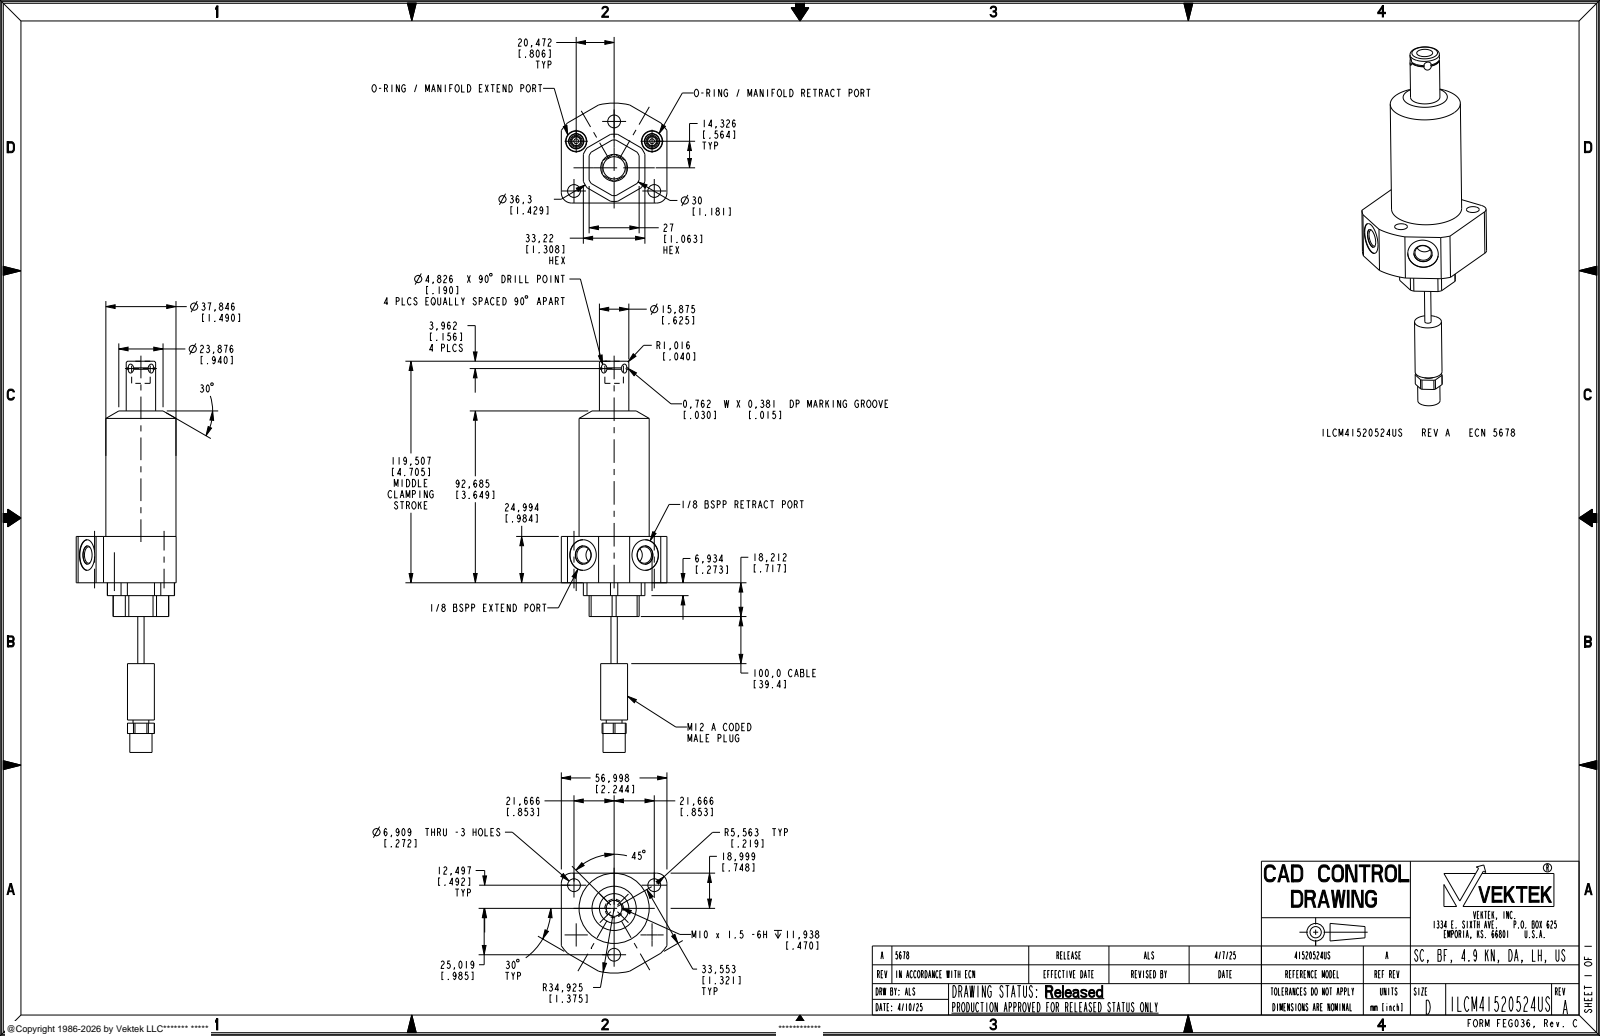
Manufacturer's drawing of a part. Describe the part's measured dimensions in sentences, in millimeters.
The part is named "ILCM41520524US". Its 3-D file was written by "CREO PARAMETRIC BY PTC INC, 2021164 (AUTOMOTIVE_DESIGN)". It is 1 solid with 184 faces: 75 planar, 79 cylindrical and 30 other. Overall it measures 211.02 by 69.92 by 65 millimeters. Its volume is 164 674 cubic millimeters and its surface area 27 750 square millimeters. Round holes: 3 of diameter 6.91, 2 of diameter 2.49, 2 of diameter 6.5, 2 of diameter 8.84, 2 of diameter 9.91, 2 of diameter 11.4, 2 of diameter 16.5, 1 of diameter 8.61. Round bosses or shafts: 2 of diameter 5.49, 1 of diameter 37.85, 1 of diameter 15.88, 1 of diameter 14.5, 1 of diameter 11.99, 1 of diameter 10.01, 1 of diameter 8.51, 1 of diameter 3.4. Partial cylindrical surfaces (rounded edges, fillets, slot ends): 2 of radius 5.56, 1 of radius 7.56, 1 of radius 15, 1 of radius 18.15, 1 of radius 34.92. The main face-to-face distances are 24.99, 57, 18.22, 43.21, 3.11, 30.11, 27, 11.28, 6.94, 31.93. The hole center spacings are 25.02, 23.09, 24.99, 26.86, 43.33, 49.96, 40.94, 43.34.
